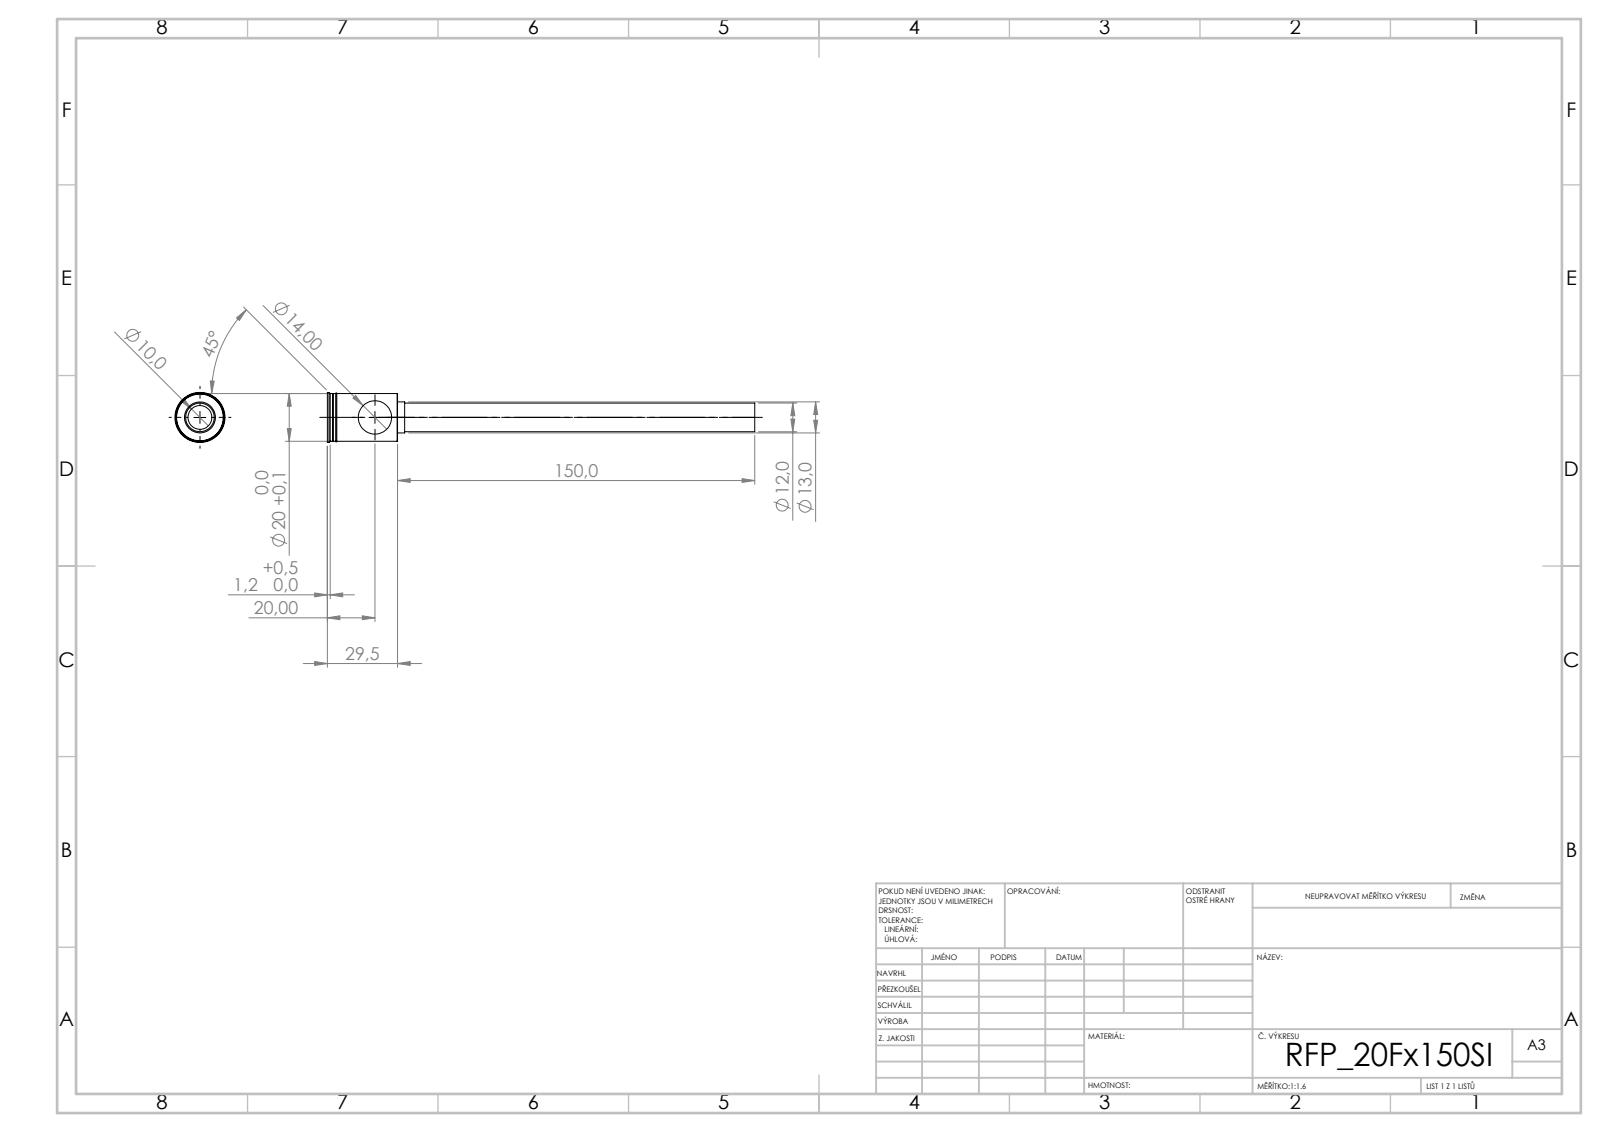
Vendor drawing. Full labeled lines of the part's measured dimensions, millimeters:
STEP written by: SolidWorks 2019 (CONFIG_CONTROL_DESIGN)
Units: millimetres
Bodies: 1 solid, 44 faces (20 planar, 16 cylindrical, 8 other)
Overall size (bounding box): 179.5 × 21 × 21
Volume: 11 022 mm³ · Surface area: 13 426 mm²
Round holes (diameter × count): ⌀10 ×1, ⌀14 ×1
Round bosses / shafts (diameter × count): ⌀21 ×1, ⌀20 ×1, ⌀13 ×1, ⌀12 ×1
Main face-to-face distances: 27.5, 2, 29.5, 15.4, 150, 177.5, 179.5, 0.5, 147, 3
